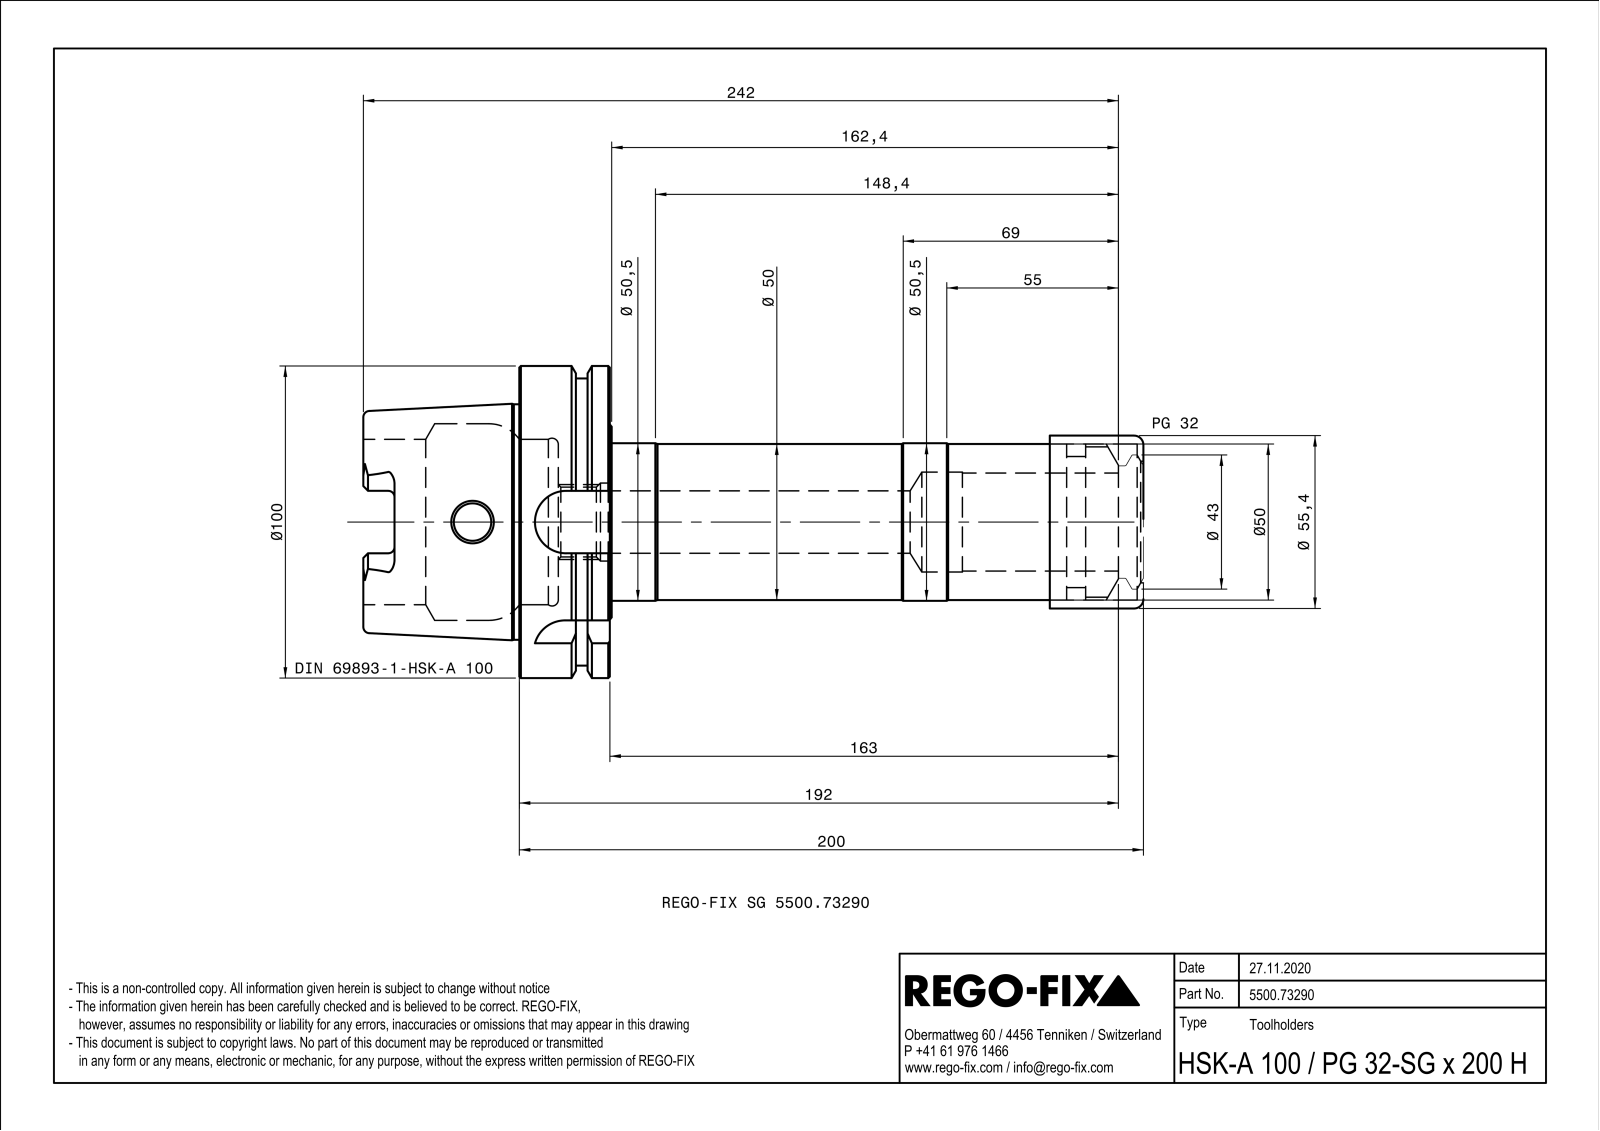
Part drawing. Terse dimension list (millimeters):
name: NOCUT
written by: SIEMENS PLM Software Solid Edge ST10 (AUTOMOTIVE_DESIGN)
unit: mm
bodies: 1 solid, 155 faces (42 planar, 44 cylindrical, 69 other)
size: 250 × 100 × 100
volume: 503 402 mm³; area: 97 263 mm²
holes: 2× ⌀12, 1× ⌀8.5, 1× ⌀10, 1× ⌀20, 1× ⌀22.38, 1× ⌀25, 1× ⌀33, 1× ⌀38.25, 1× ⌀48.38, 1× ⌀50.05, 1× ⌀51, 1× ⌀53
bosses: 1× ⌀100, 1× ⌀92, 1× ⌀75.46, 1× ⌀55.4, 1× ⌀55, 1× ⌀50.5, 1× ⌀50, 1× ⌀42
rounds: 6× R2, 4× R4.88, 2× R10, 1× R11
face distances: 29, 16.5, 12.5, 50, 79, 62.5, 171, 187.5, 200, 250
